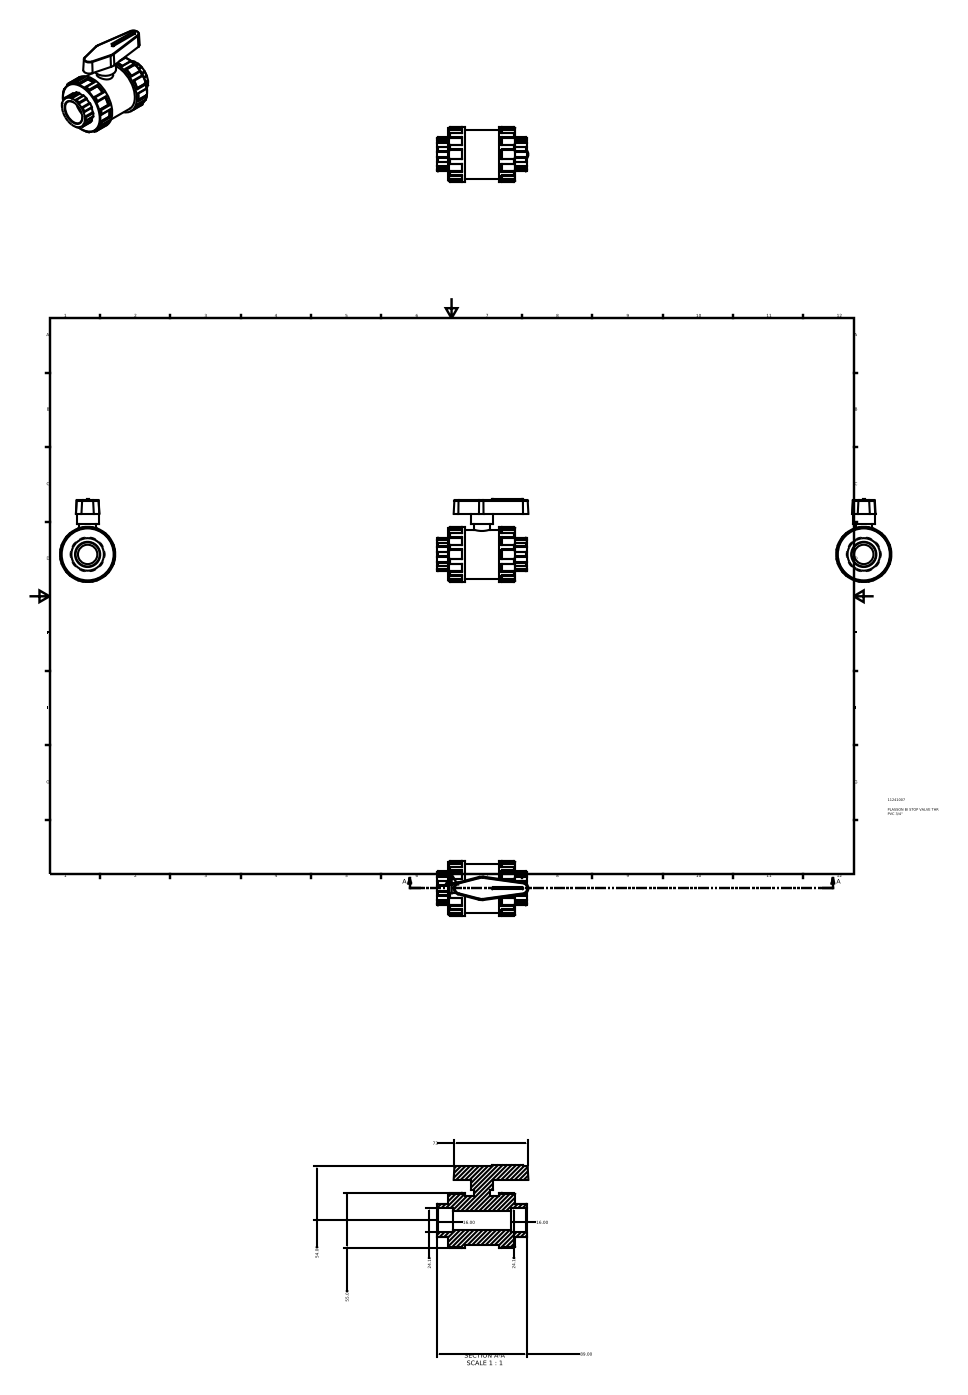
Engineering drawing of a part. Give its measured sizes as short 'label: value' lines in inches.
name: 11241007
written by: Autodesk Inventor 2015 (AUTOMOTIVE_DESIGN)
unit: in
bodies: 1 solid, 434 faces (114 planar, 192 cylindrical, 128 other)
size: 3.575 × 3.272 × 2.165
volume: 9.071 in³; area: 46.06 in²
holes: 1× ⌀0.759, 1× ⌀0.95
bosses: 1× ⌀2.165, 1× ⌀2.079, 1× ⌀1.949, 1× ⌀0.866, 1× ⌀0.65
rounds: 76× R0.028, 4× R0.019, 2× R0.043, 1× R0.636, 1× R0.665
face distances: 2.622, 0.63, 0.441, 2.433, 1.992, 0.531, 1.071, 3.063, 1.362, 2.874
